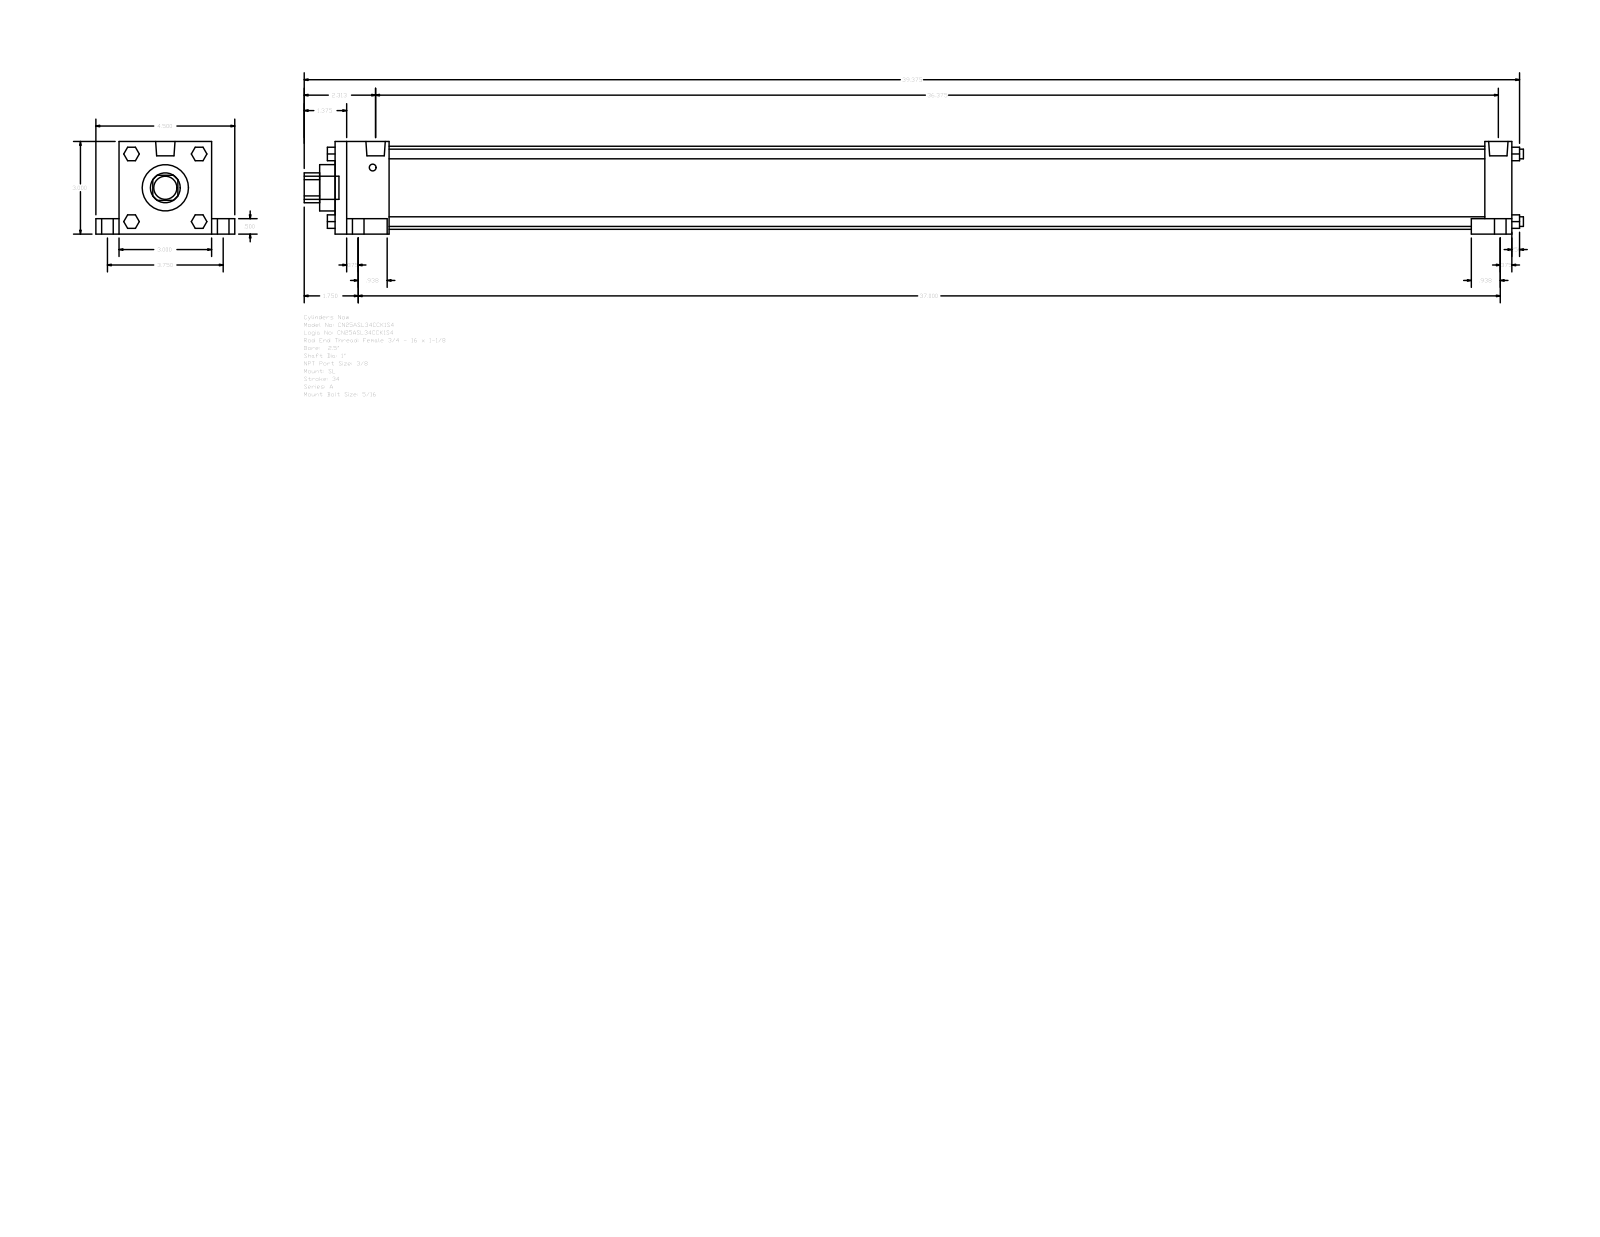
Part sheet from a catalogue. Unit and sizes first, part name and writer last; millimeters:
Units: millimetres
Overall size (bounding box): 1003.3 × 114.3 × 76.2
Round holes (diameter × count): ⌀25.4 ×1, ⌀38.1 ×1, ⌀68.33 ×1
Round bosses / shafts (diameter × count): ⌀15.88 ×4, ⌀9.53 ×4, ⌀7.94 ×4, ⌀5.56 ×4, ⌀15.93 ×2, ⌀19.05 ×1
Partial cylindrical surfaces — rounded edges, fillets, slot ends (radius × count): R12.29 ×1
Main face-to-face distances: 76.2, 968.37, 12.7, 22.22, 44.45, 923.92, 946.15, 901.7, 19.05, 63.5
Bodies: 0 solids, 148 faces (112 planar, 36 cylindrical, 0 other)
Part name (STEP PRODUCT): A_SL__0250_1
STEP written by: GSSL Pune (CONFIG_CONTROL_DESIGN)
